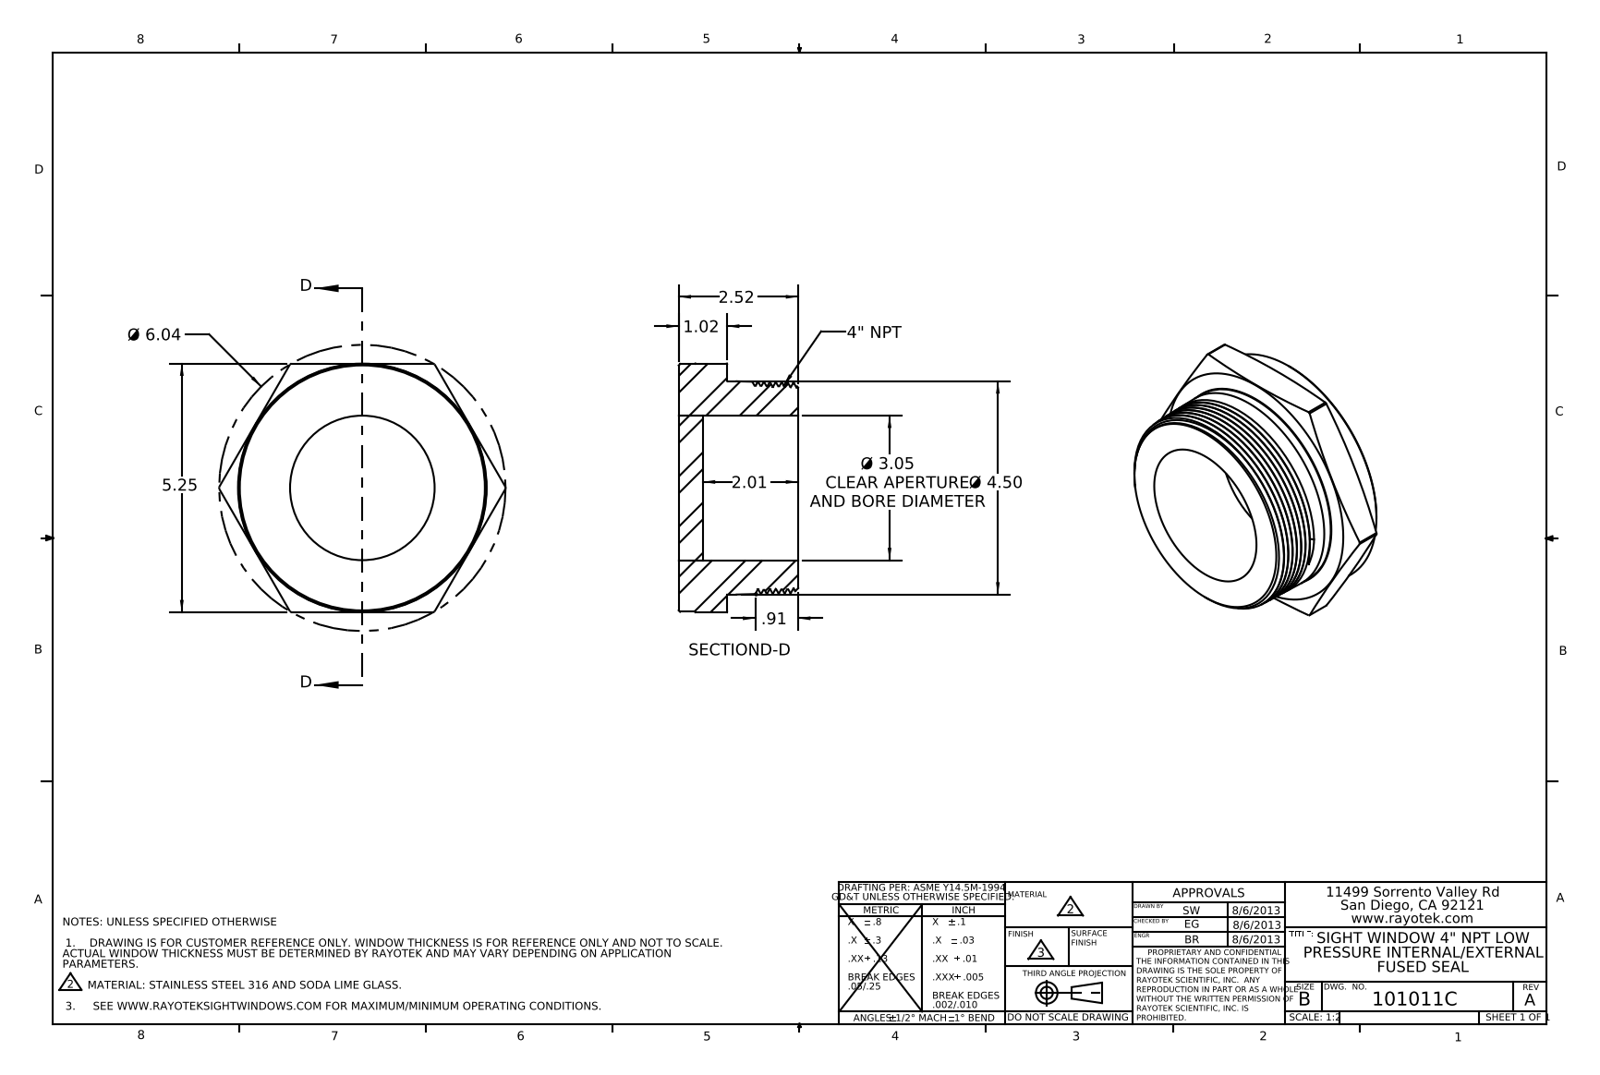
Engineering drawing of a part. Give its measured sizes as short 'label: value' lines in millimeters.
name: 403011
written by: SolidWorks 2012 (AUTOMOTIVE_DESIGN)
unit: mm
bodies: 2 solids, 60 faces (14 planar, 15 cylindrical, 31 other)
size: 153.5 × 133.4 × 64
volume: 517 800 mm³; area: 79 740 mm²
holes: 1× ⌀77.5
bosses: 1× ⌀132.8, 1× ⌀114.3
rounds: 1× R76.7
face distances: 13, 64, 51.1, 133.4, 25.9, 13, 38.1
